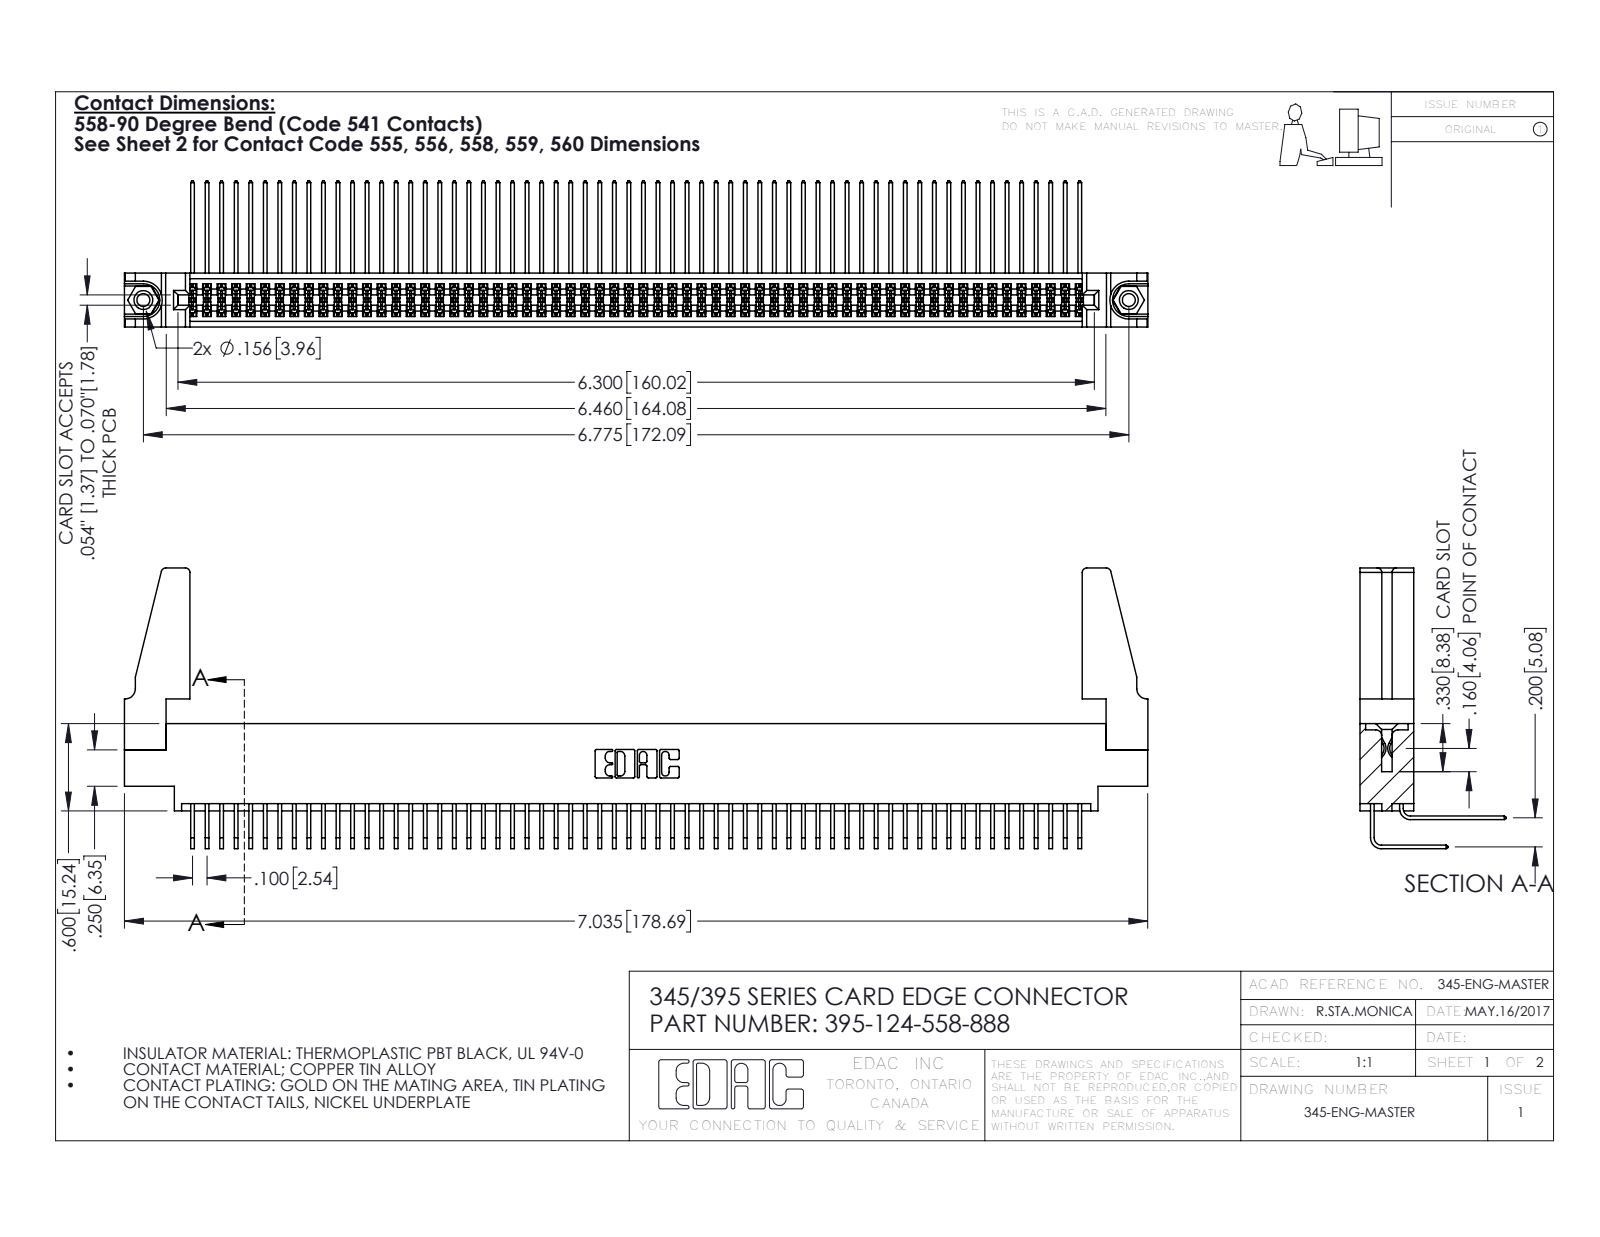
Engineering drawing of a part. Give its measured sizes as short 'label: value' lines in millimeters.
name: 345-292-001_558 559 Tail - 1; 345-220-078_345-220-088; 345-250-001_345-250-001-102; 345 Part_0.170 Offset - 0.156 Dia-TH (+2 more)
written by: SolidWorks 2016 (CONFIG_CONTROL_DESIGN)
unit: mm
bodies: 129 solids, 6702 faces (4496 planar, 2190 cylindrical, 16 other)
size: 178.7 × 49 × 25.5
volume: 21 400 mm³; area: 33 850 mm²
holes: 2× ⌀2.3, 2× ⌀3.2, 2× ⌀4, 1× ⌀1.6
bosses: 2× ⌀3.9
rounds: 187× R0.2, 22× R0.3, 8× R0.8, 6× R0.2, 6× R0.8, 3× R0.7, 2× R0.4, 2× R0.5
face distances: 1.8, 7.6, 5.1, 9.4, 2.5, 6.9, 0.6, 5.7, 4.4, 0.6
hole spacings: 6.9, 166.1, 172.1
